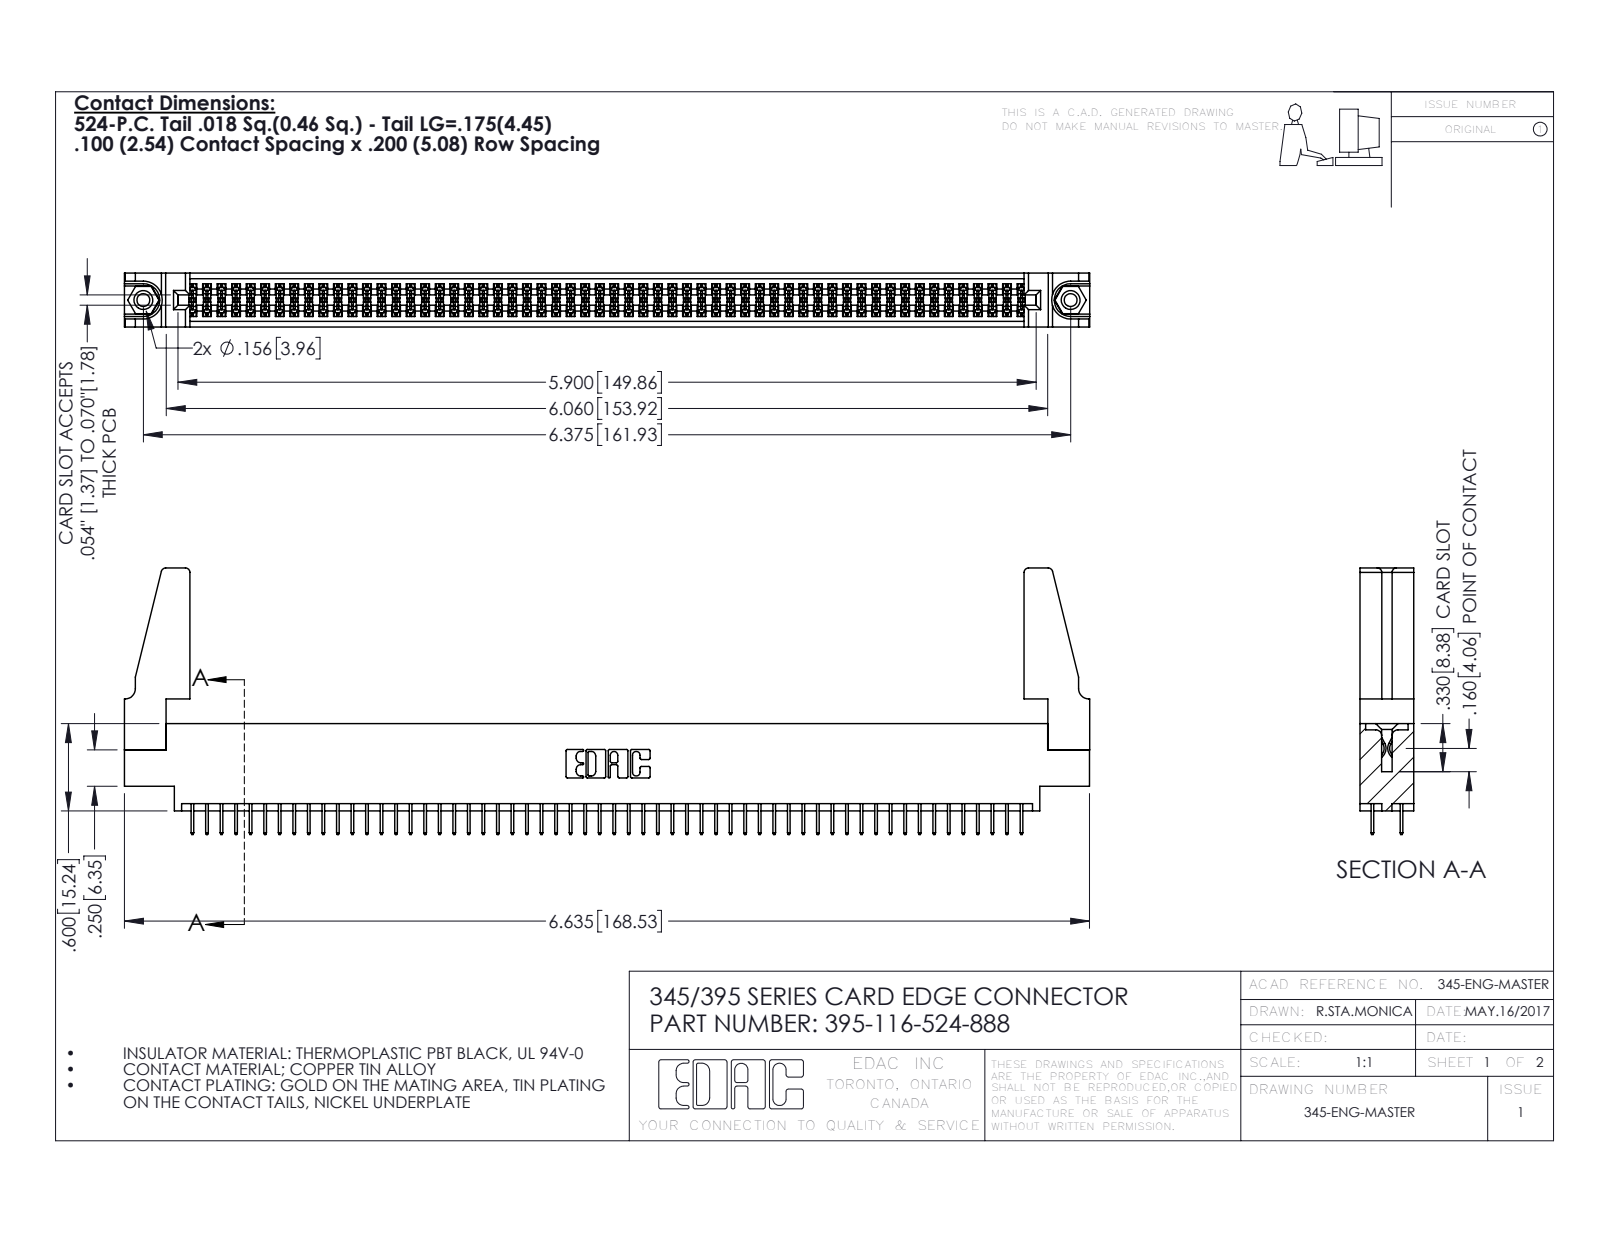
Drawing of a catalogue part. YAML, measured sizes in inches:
part_name: "345-250-001_345-250-001-102; 395-116-524-888; 345-292-001_345-293-124; 345 Part_0.170 Offset - 0.156 Dia-TH (+1 more)"
step_written_by: "SolidWorks 2016 (CONFIG_CONTROL_DESIGN)"
units: inches
bodies: {solids: 121, faces: 6518, planar: 4680, cylindrical: 1822, other: 16}
overall_size: [6.636, 1.832, 0.37]
volume: 1.189
surface_area: 42.02
round_holes:
  - {diameter: 0.089, count: 2}
  - {diameter: 0.125, count: 2}
  - {diameter: 0.156, count: 2}
  - {diameter: 0.064, count: 1}
round_bosses_or_shafts:
  - {diameter: 0.155, count: 2}
partial_cylinders:
  - {radius: 0.006, count: 174}
  - {radius: 0.01, count: 22}
  - {radius: 0.03, count: 8}
  - {radius: 0.007, count: 6}
  - {radius: 0.031, count: 6}
  - {radius: 0.026, count: 3}
  - {radius: 0.014, count: 2}
  - {radius: 0.019, count: 2}
face_to_face_distances: [0.072, 0.298, 0.37, 0.2, 0.098, 0.272, 0.025, 0.225, 0.072, 0.175]
hole_center_spacings: [0.27, 6.139, 6.375]
